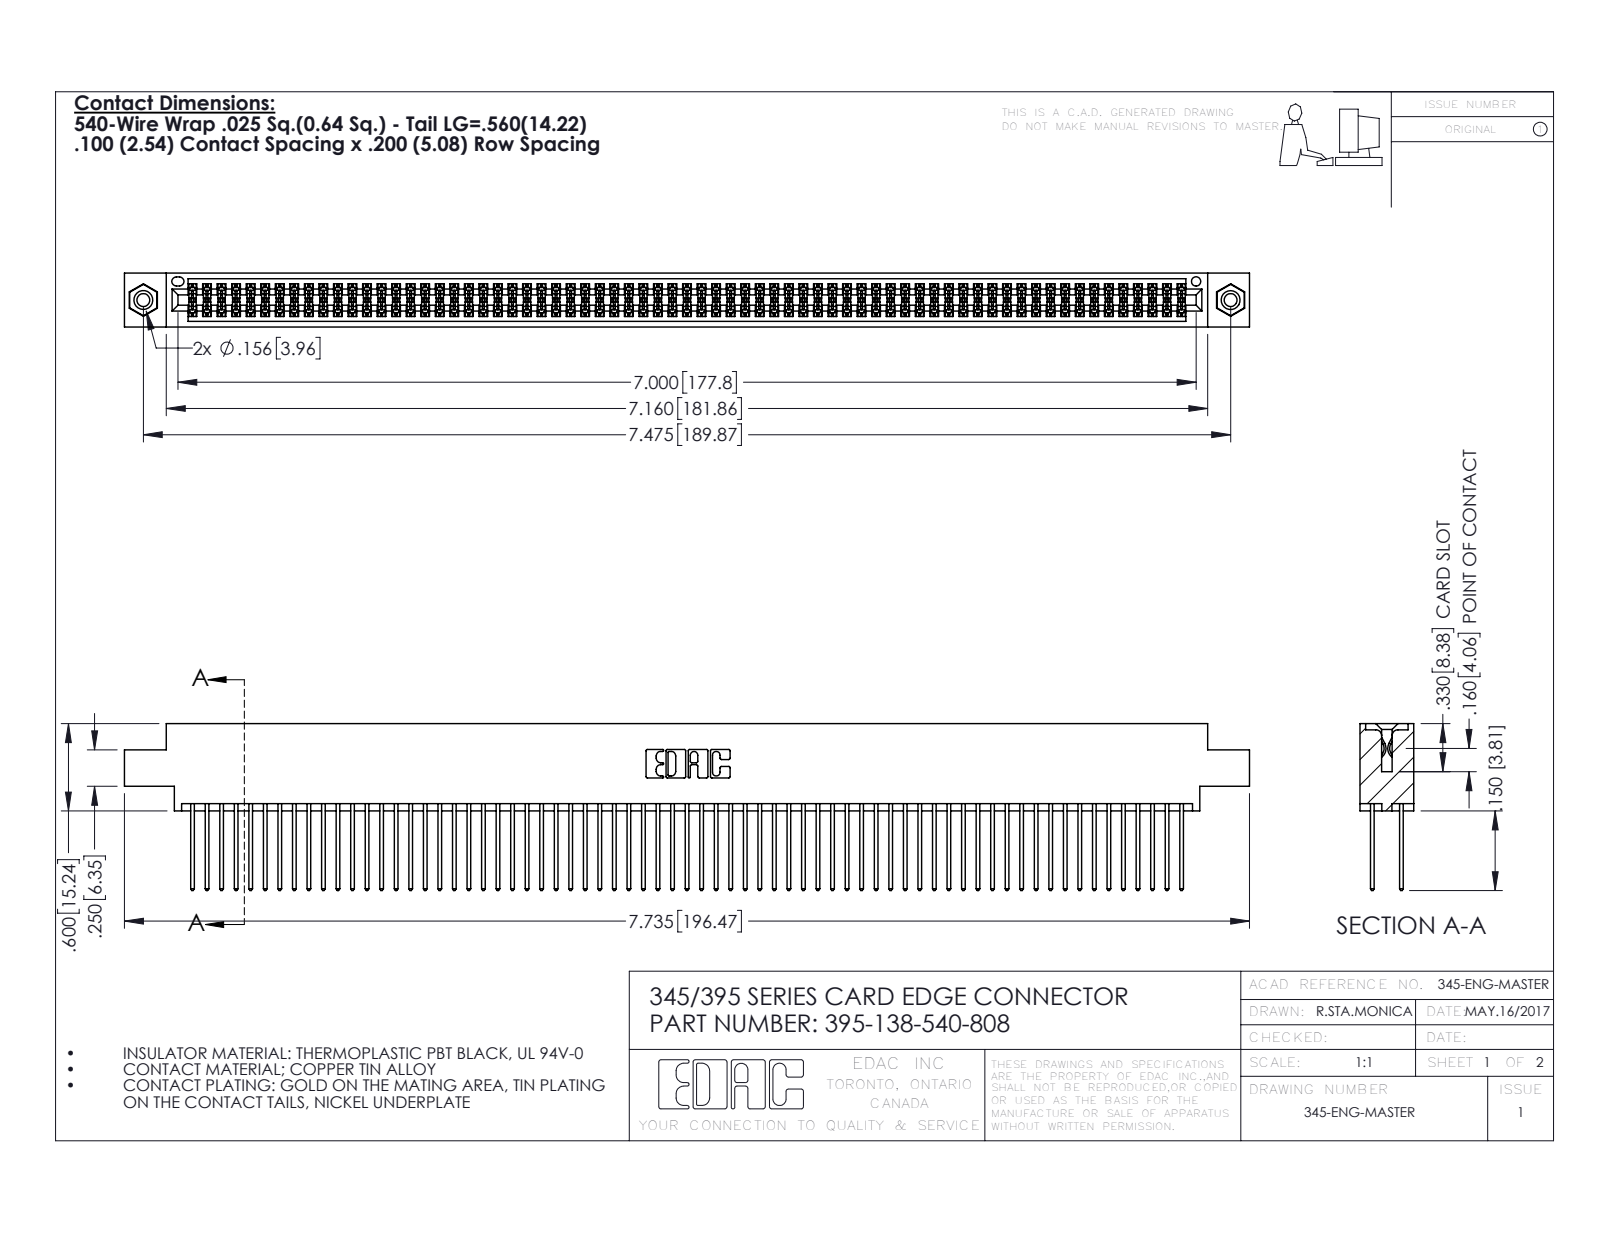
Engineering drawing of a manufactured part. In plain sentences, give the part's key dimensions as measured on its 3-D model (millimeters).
The part is named "345 Part_0.170 Offset - 0.156 Dia-TI; 345-292-001_345-293-140; 345-250-001_345-250-003-102; 395-138-540-808". Its 3-D file was written by "SolidWorks 2016 (CONFIG_CONTROL_DESIGN)". It is 141 solids with 7090 faces: 4670 planar, 2404 cylindrical and 16 other. Overall it measures 196.5 by 29.1 by 9.4 millimeters. Its volume is 19 750 cubic millimeters and its surface area 32 280 square millimeters. Round holes: 2 of diameter 2.3, 2 of diameter 3.2, 2 of diameter 4, 1 of diameter 1.6. Round bosses or shafts: 2 of diameter 3.9. Partial cylindrical surfaces (rounded edges, fillets, slot ends): 207 of radius 0.2, 138 of radius 0.3, 22 of radius 0.3, 6 of radius 0.2, 6 of radius 0.8, 3 of radius 0.7, 2 of radius 0.4, 2 of radius 0.5. The main face-to-face distances are 1.8, 7.6, 5.1, 2.5, 6.9, 0.6, 9.4, 5.7, 4.4, 3.8. The hole center spacings are 6.9, 183.9, 189.9.
